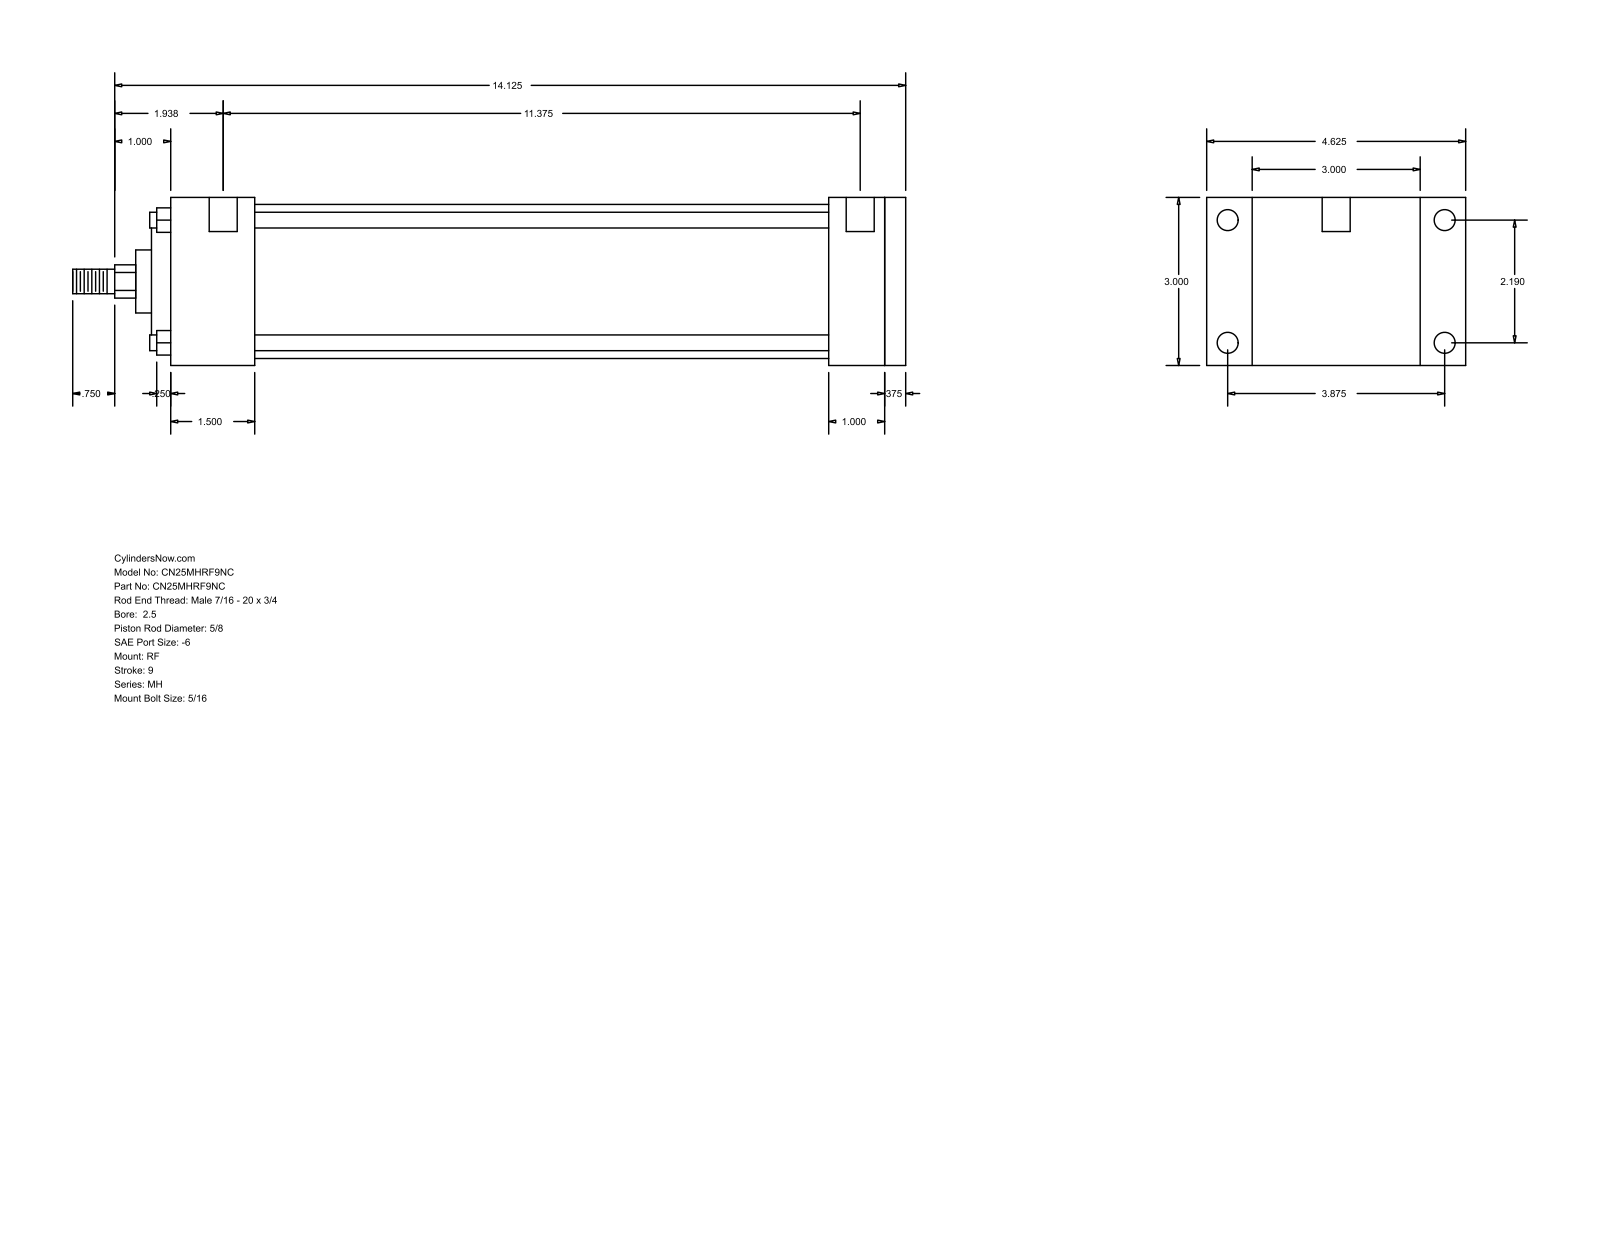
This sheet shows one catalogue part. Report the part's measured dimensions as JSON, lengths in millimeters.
{"part_name": "MH_RF__0250_0.625", "step_written_by": "GSSL Pune (CONFIG_CONTROL_DESIGN)", "units": "millimeters", "bodies": {"solids": 0, "faces": 94, "planar": 65, "cylindrical": 29, "other": 0}, "overall_size": [377.82, 117.47, 76.2], "round_holes": [[5.56, 4], [9.53, 4], [12.7, 2]], "round_bosses_or_shafts": [[7.14, 4], [69.85, 1], [55.55, 1], [28.57, 1], [15.88, 1], [11.11, 1]], "partial_cylinders_radius": [[7.54, 1]], "face_to_face_distances": [76.2, 9.52, 333.37, 323.85, 25.4, 38.1, 298.45, 34.92, 260.35, 285.75], "hole_center_spacings": [55.62, 98.42, 113.05, 296.86, 3.17, 4.76, 288.93, 292.1]}
